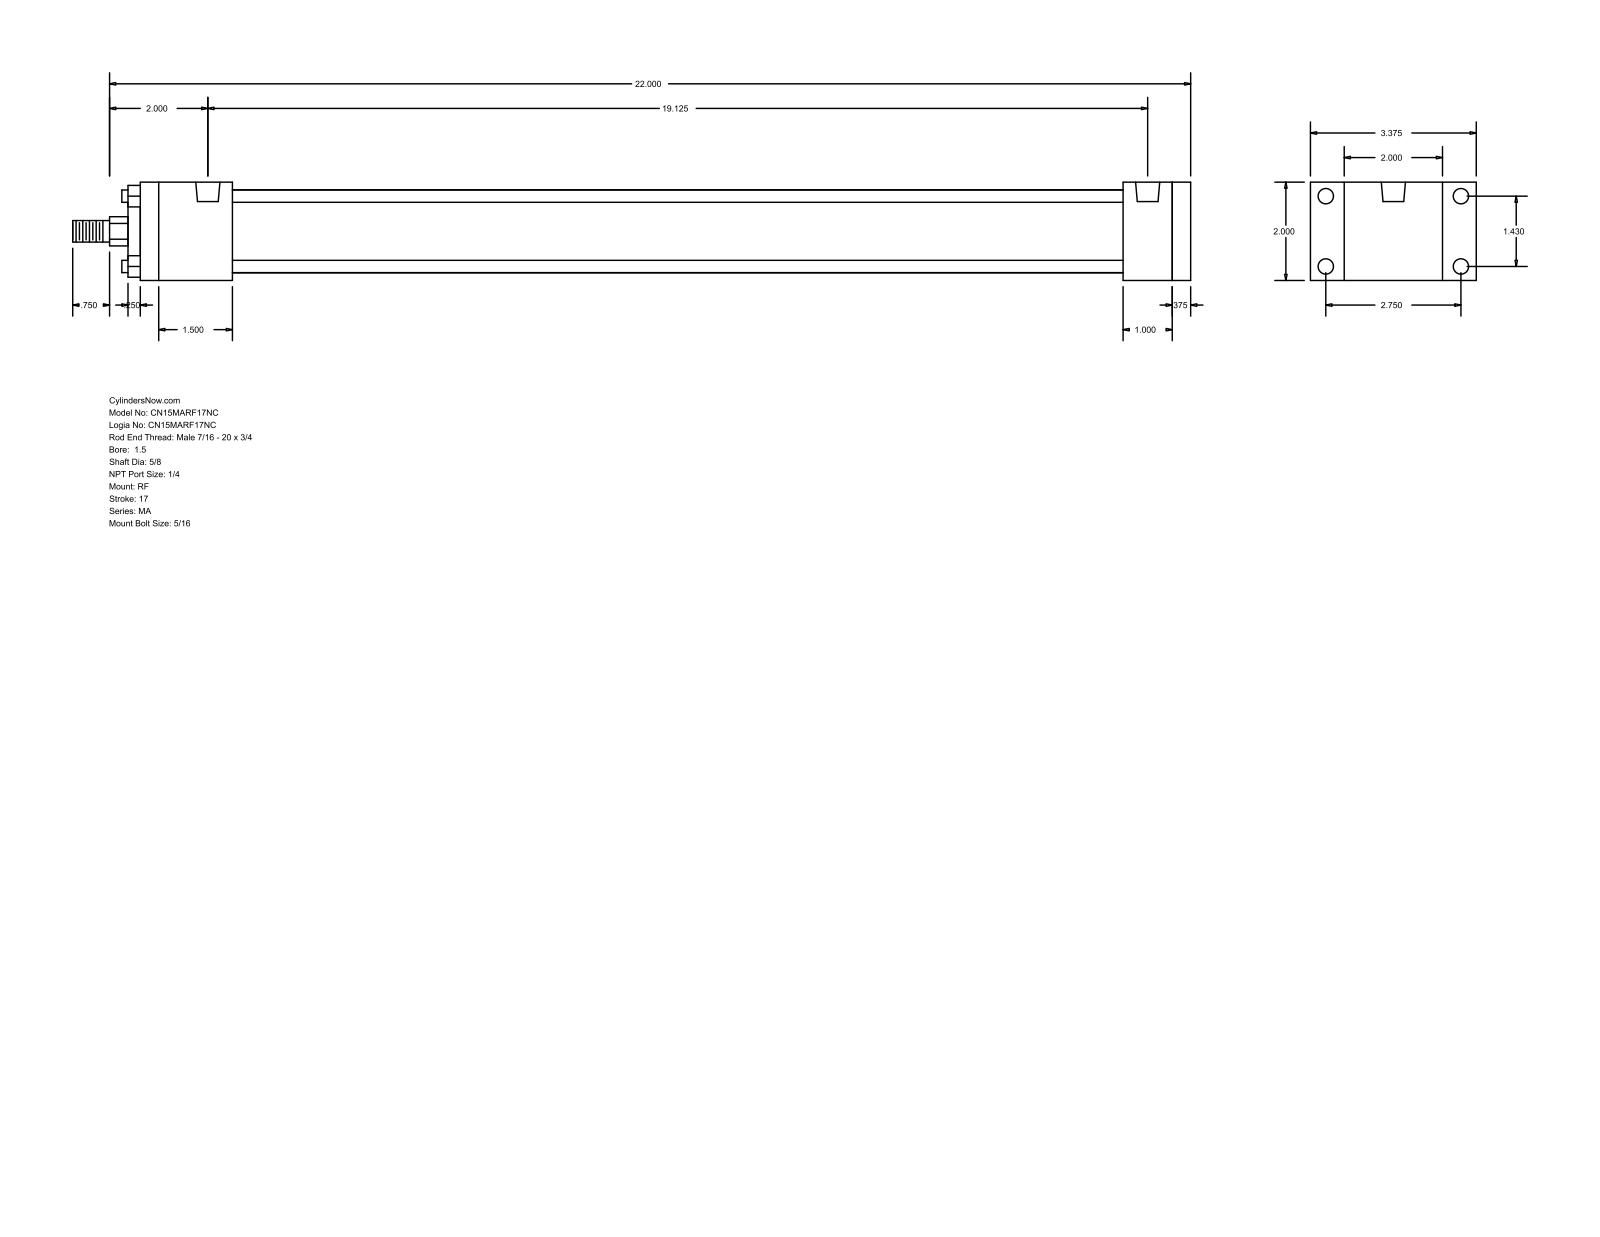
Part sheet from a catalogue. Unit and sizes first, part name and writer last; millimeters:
Units: millimetres
Overall size (bounding box): 577.85 × 85.72 × 50.8
Round holes (diameter × count): ⌀7.94 ×8, ⌀12.49 ×2
Round bosses / shafts (diameter × count): ⌀6.35 ×4, ⌀42.93 ×1, ⌀28.57 ×1, ⌀15.88 ×1, ⌀11.11 ×1
Partial cylindrical surfaces — rounded edges, fillets, slot ends (radius × count): R7.54 ×1
Main face-to-face distances: 50.8, 9.53, 542.92, 533.39, 508, 25.39, 34.92, 47.62, 460.38, 485.77
Hole centre spacings: 36.32, 69.84, 78.72, 485.78
Bodies: 0 solids, 92 faces (64 planar, 28 cylindrical, 0 other)
Part name (STEP PRODUCT): MA_RF__0150_0.625
STEP written by: GSSL Pune (CONFIG_CONTROL_DESIGN)
